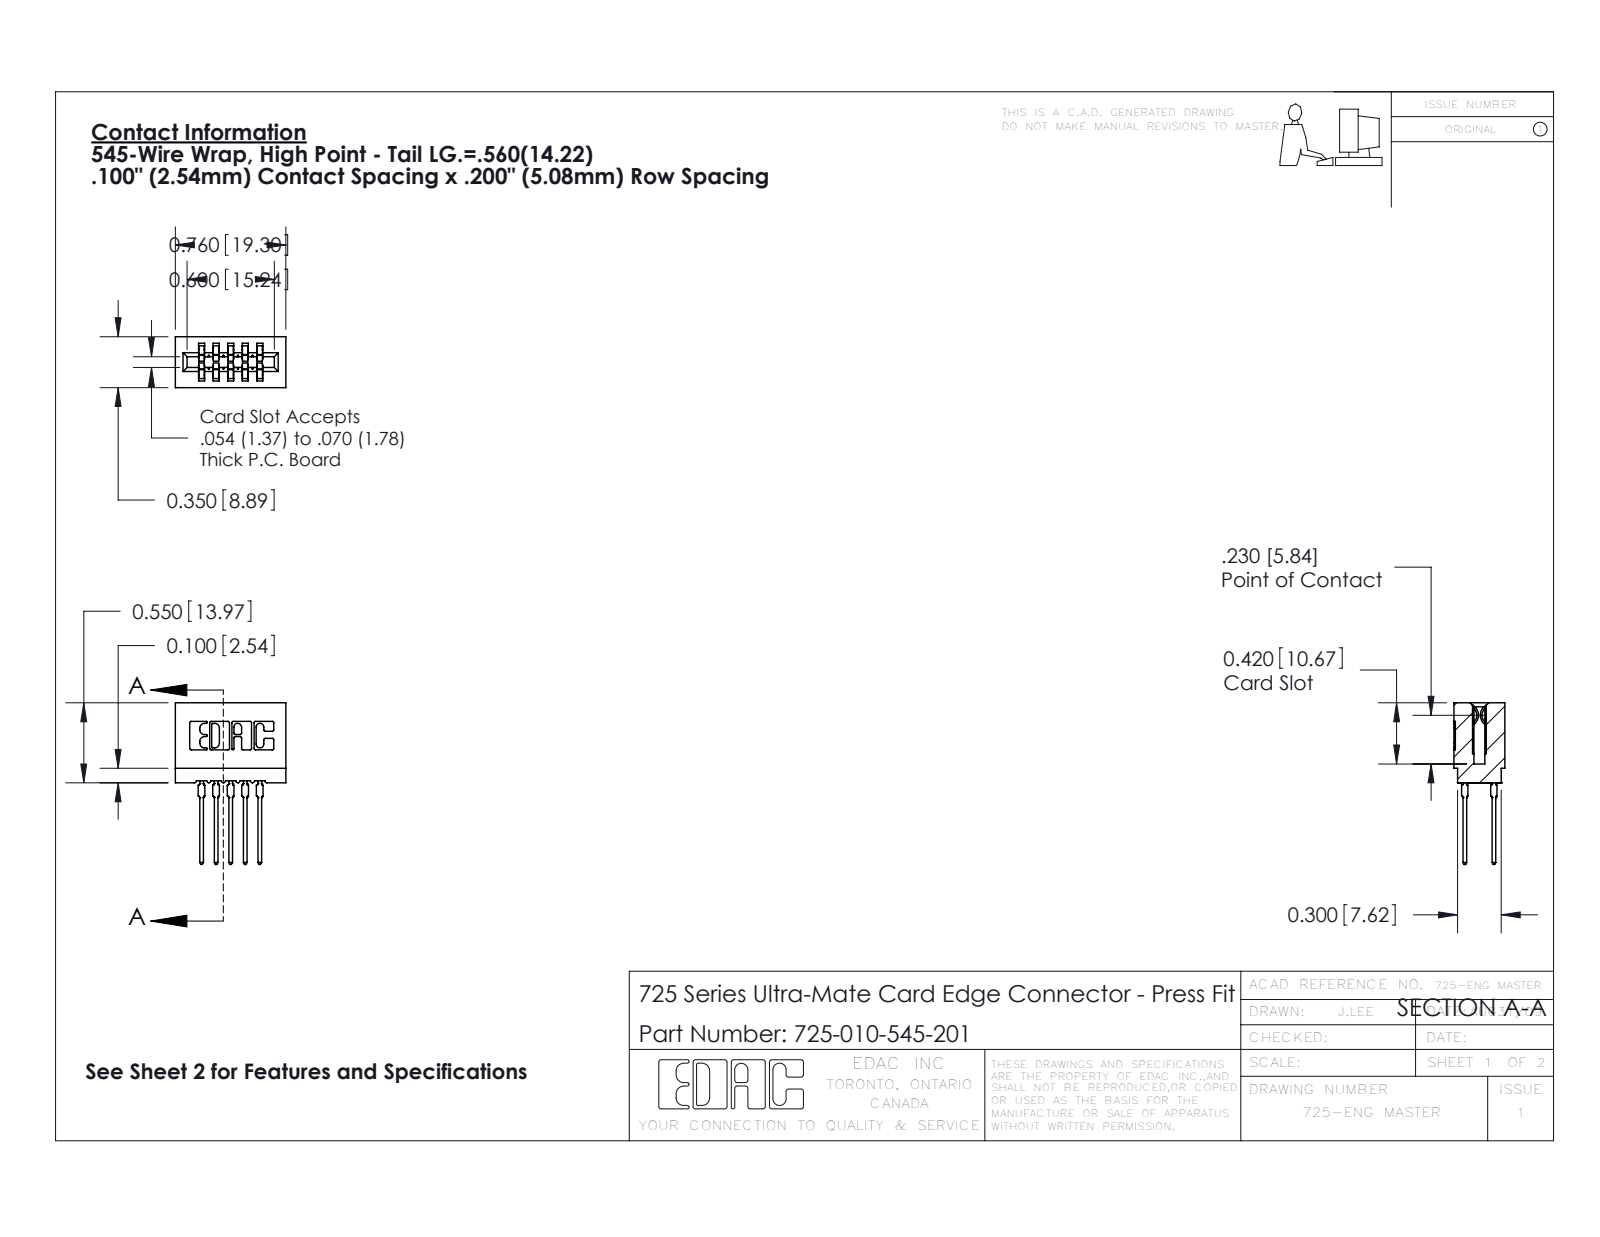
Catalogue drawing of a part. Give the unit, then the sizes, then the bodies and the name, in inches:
Units: inches
Overall size (bounding box): 1.11 × 0.76 × 0.35
Partial cylindrical surfaces — rounded edges, fillets, slot ends (radius × count): R0.01 ×22, R0.021 ×20, R0.015 ×10, R0.005 ×8, R0.011 ×8, R0.007 ×6, R0.031 ×6, R0.026 ×3
Main face-to-face distances: 0.1, 0.2, 0.042, 0.3, 0.142, 0.058, 0.287, 0.063, 0.242, 0.158
Volume: 0.107 in³ · Surface area: 4.747 in²
Bodies: 11 solids, 990 faces (515 planar, 215 cylindrical, 260 other)
Part name (STEP PRODUCT): 725 Part_Insulator Option - 01; 745-292-001_545; 725-010-545-201
STEP written by: SolidWorks 2016 (CONFIG_CONTROL_DESIGN)
